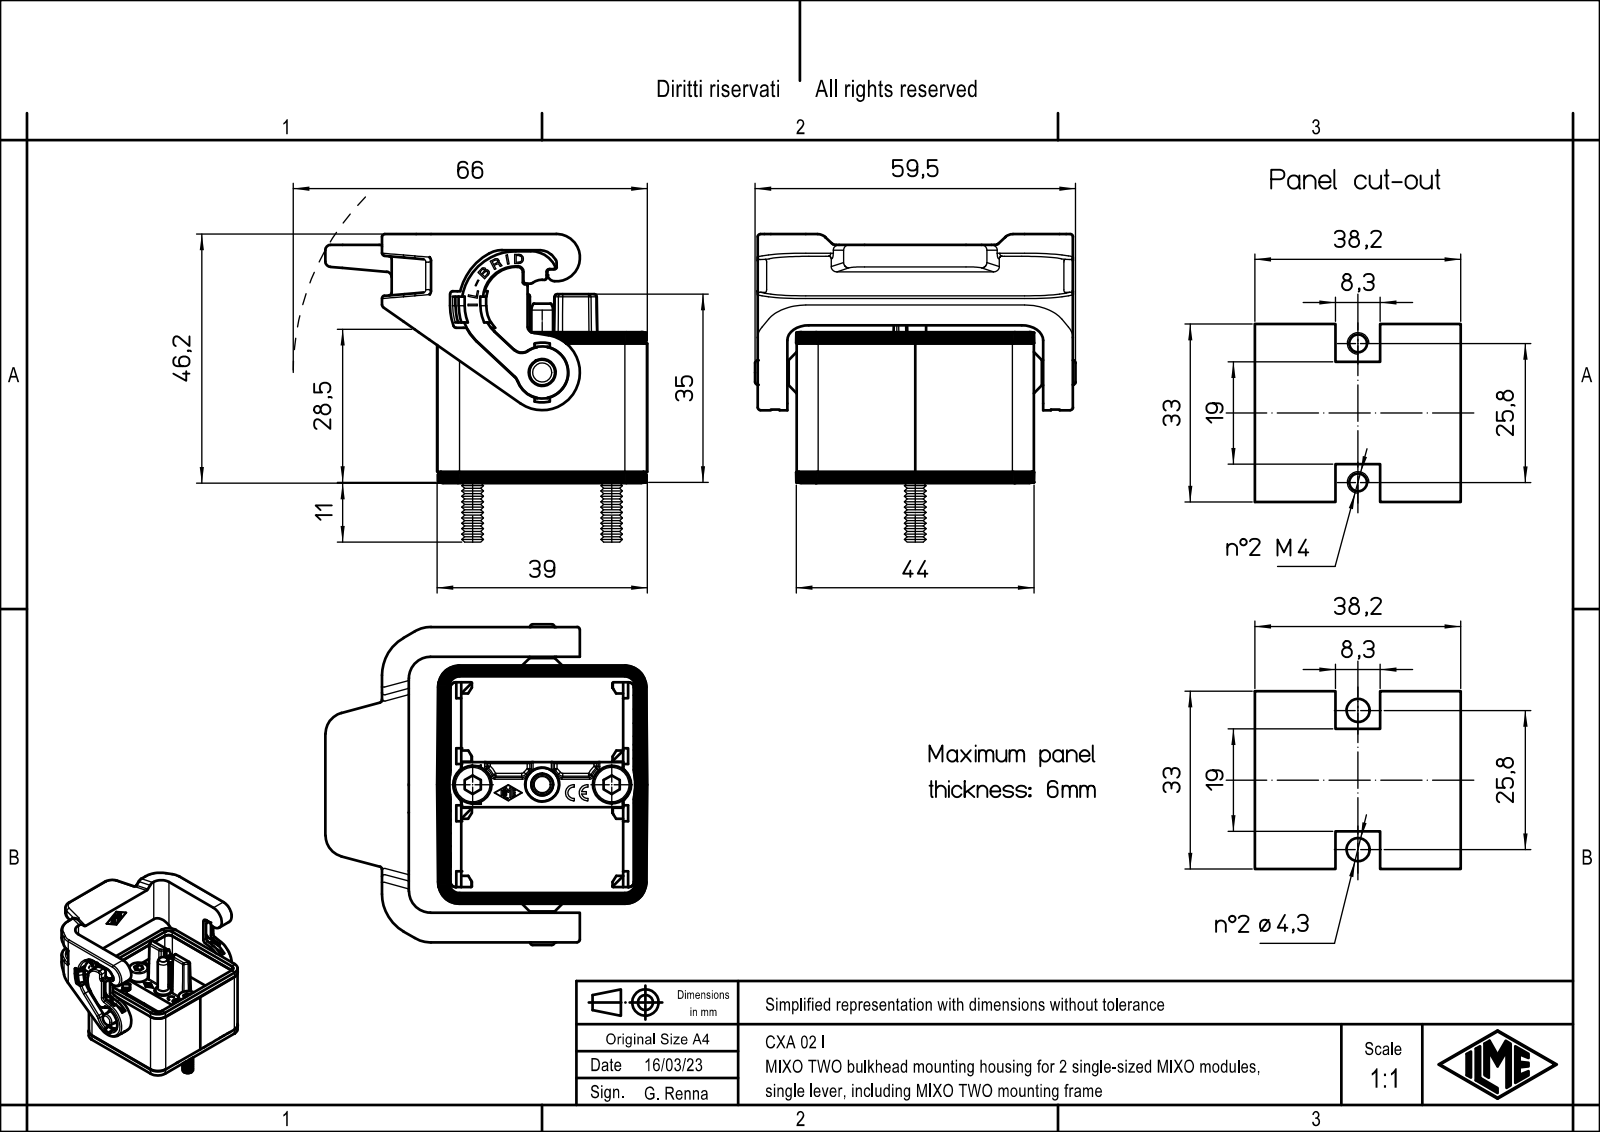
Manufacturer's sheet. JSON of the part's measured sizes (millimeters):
{"part_name": "CXA 02 I", "step_written_by": "Creo Elements/Direct Modeling 20.1B 02-Apr-2019 (C) Parametric Technology GmbH (AUTOMOTIVE_DESIGN)", "units": "millimeters", "bodies": {"solids": 1, "faces": 2173, "planar": 1050, "cylindrical": 541, "other": 582}, "overall_size": [59.75, 59.5, 57.15], "volume_mm3": 25629, "surface_area_mm2": 26270, "round_holes": [[4.2, 2], [3, 1], [5.4, 1]], "round_bosses_or_shafts": [[4, 4], [7, 2], [6, 1], [3.6, 1], [2.71, 1]], "partial_cylinders_radius": [[0.1, 76], [0.5, 74], [1, 49], [0.3, 32], [0.2, 30], [2, 25], [1.5, 14], [3, 12]], "face_to_face_distances": [1.75, 45.75, 39, 5.5, 44, 2, 7.25, 51.25, 53, 47.5], "hole_center_spacings": [5.4, 20.4, 25.8]}
